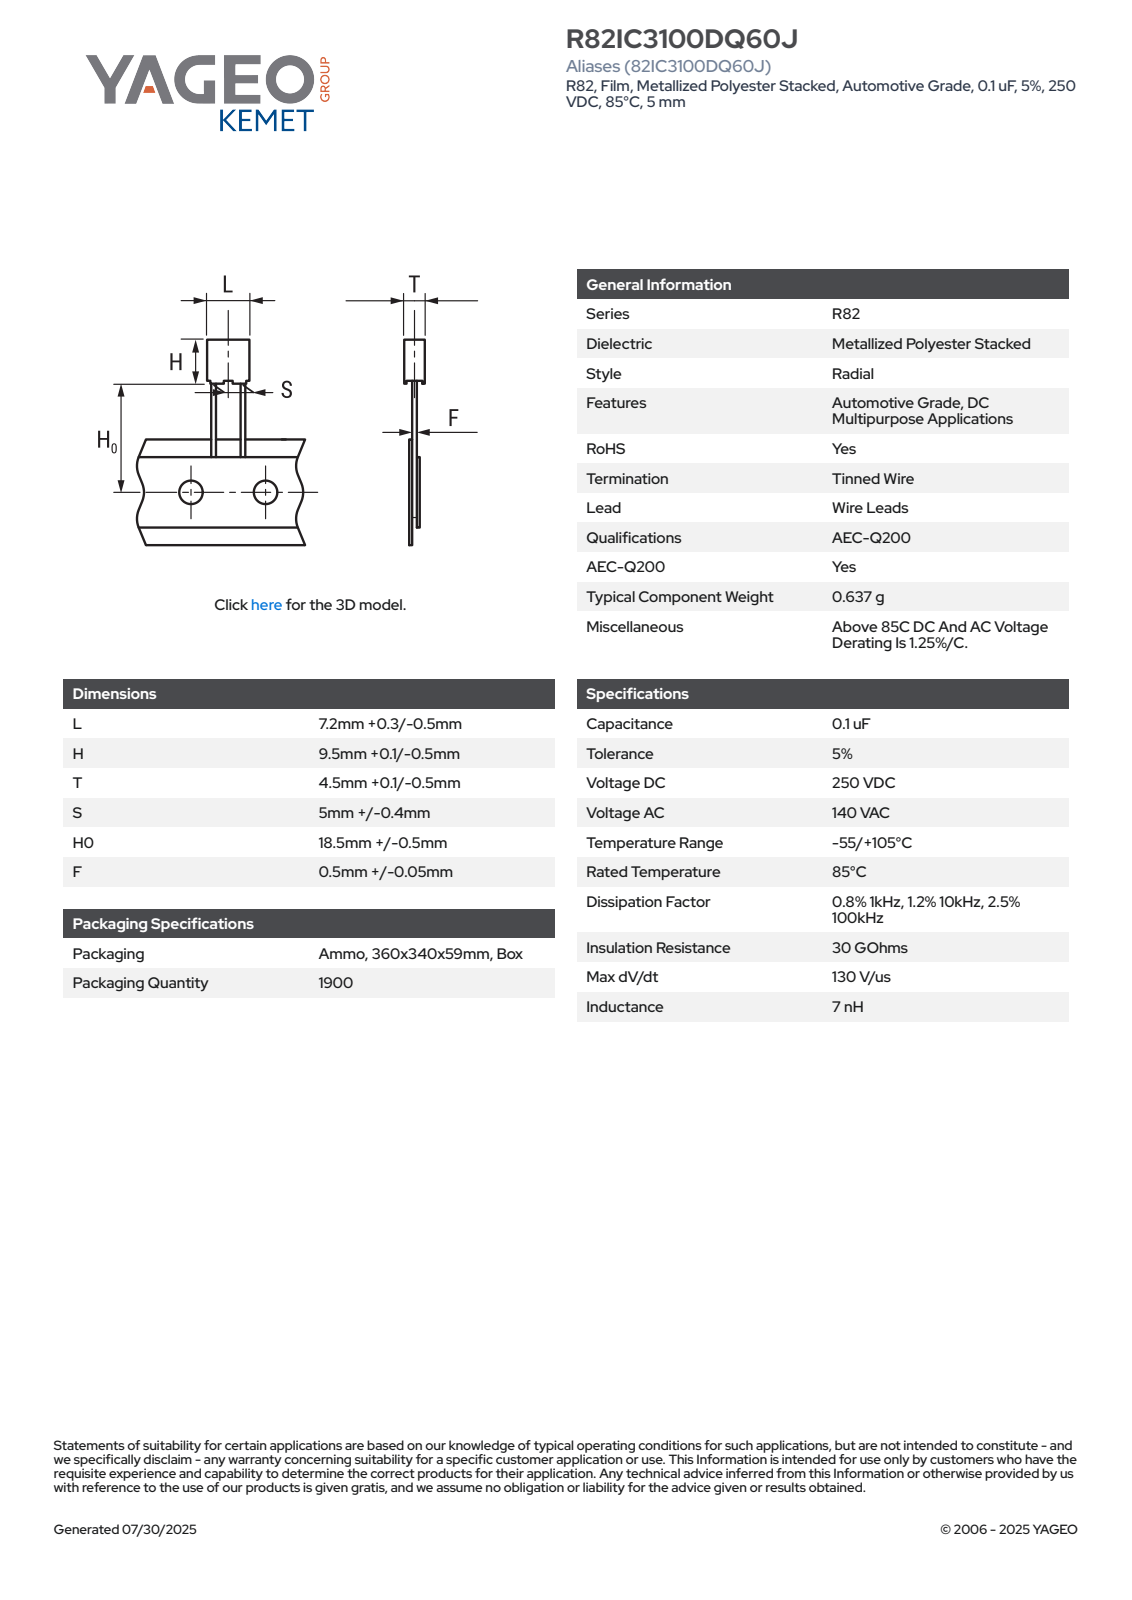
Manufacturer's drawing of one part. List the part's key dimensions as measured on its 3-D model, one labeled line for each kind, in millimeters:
Part name (STEP PRODUCT): CFR_RB3_7.2X9.5X4.5_L7.5H9.6T4.6S5H019F0.55
STEP written by: SolidWorks 2021 (AUTOMOTIVE_DESIGN)
Units: millimetres
Bodies: 4 solids, 85 faces (77 planar, 8 cylindrical, 0 other)
Overall size (bounding box): 28.6 × 7.5 × 4.61
Volume: 318 mm³ · Surface area: 383 mm²
Round bosses / shafts (diameter × count): ⌀0.55 ×2
Partial cylindrical surfaces — rounded edges, fillets, slot ends (radius × count): R0.5 ×4
Main face-to-face distances: 4.6, 7.5, 8.85, 4.35, 7.25, 0.75, 9.6, 4.1, 7, 0.33
